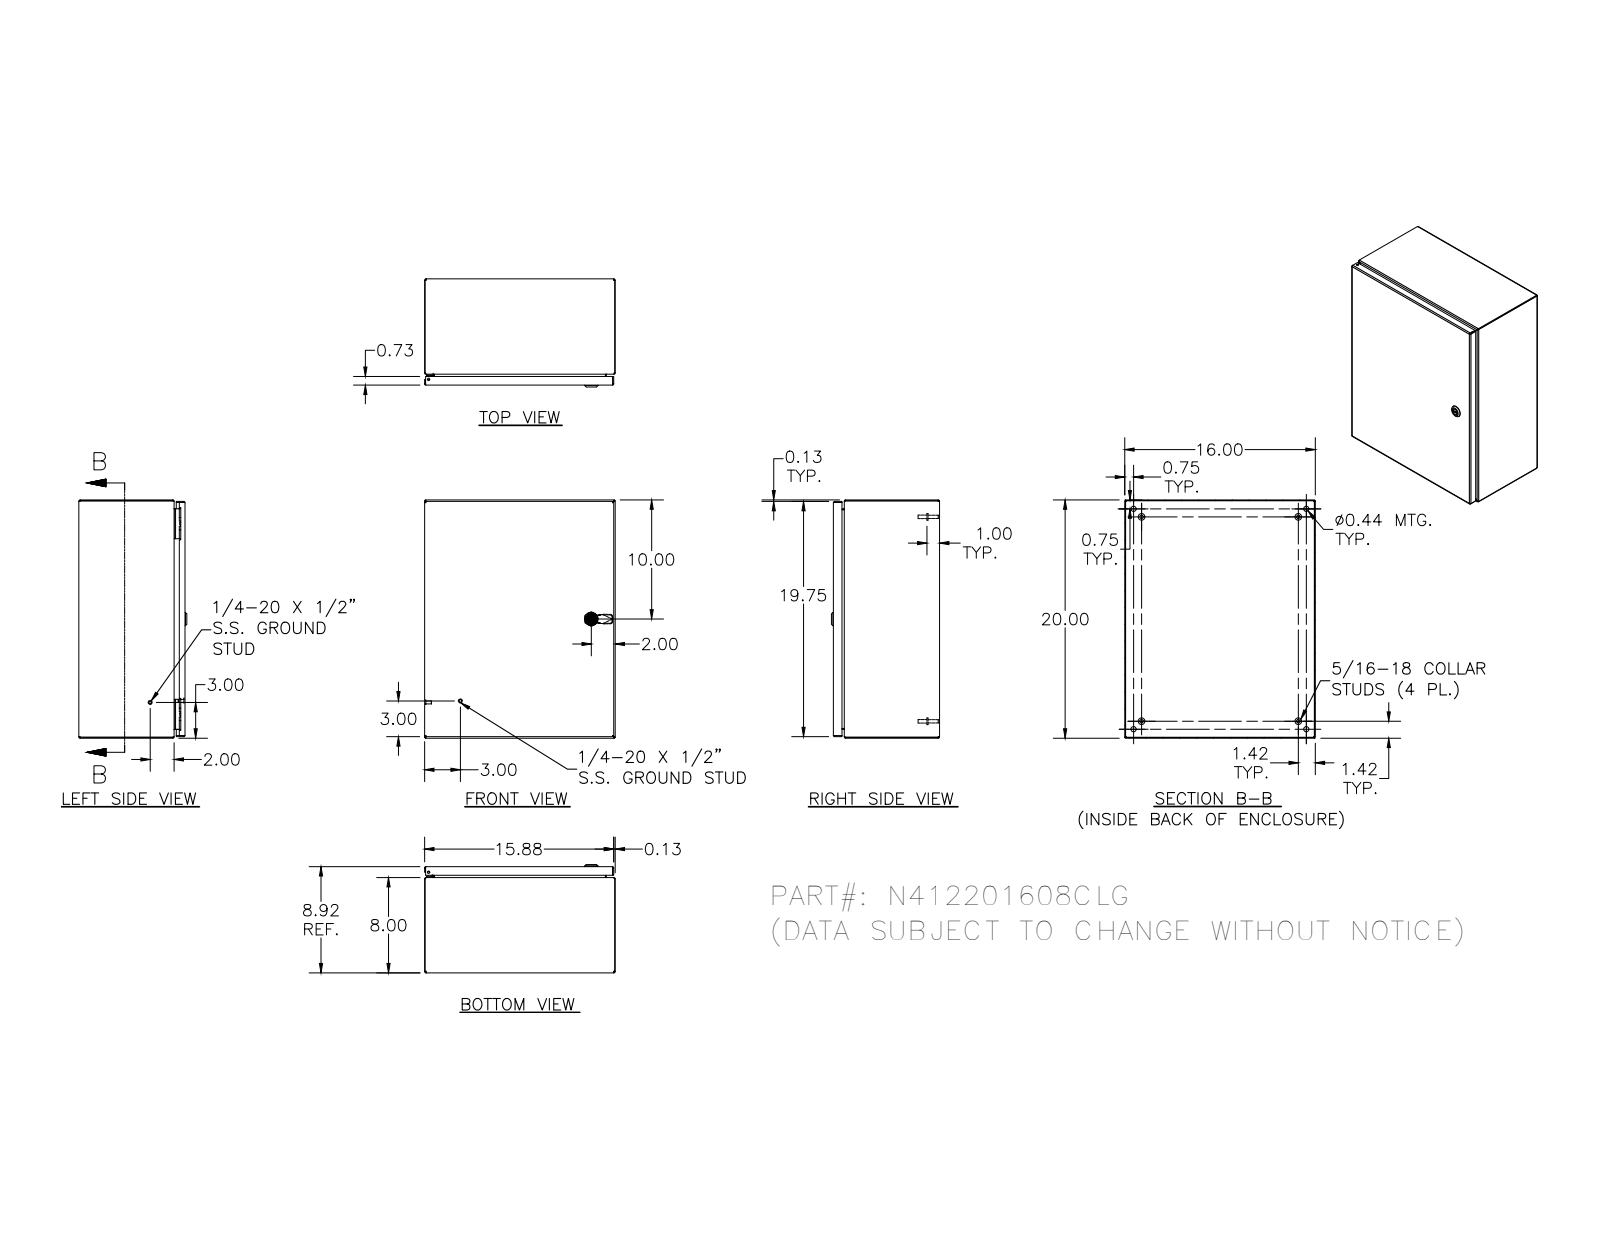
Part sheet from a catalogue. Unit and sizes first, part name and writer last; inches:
Units: inches
Overall size (bounding box): 20 × 16 × 9.075
Round holes (diameter × count): ⌀0.188 ×5, ⌀0.093 ×4, ⌀0.152 ×4, ⌀0.167 ×4, ⌀0.172 ×4, ⌀0.437 ×4, ⌀0.156 ×2, ⌀0.187 ×1, ⌀0.197 ×1, ⌀0.315 ×1, ⌀0.394 ×1, ⌀0.402 ×1
Round bosses / shafts (diameter × count): ⌀0.25 ×10, ⌀0.131 ×5, ⌀0.563 ×4, ⌀0.36 ×4, ⌀0.32 ×4, ⌀0.3 ×4, ⌀0.275 ×4, ⌀0.256 ×4
Partial cylindrical surfaces — rounded edges, fillets, slot ends (radius × count): R0.012 ×30, R0.031 ×30, R0.05 ×26, R0.105 ×20, R0.016 ×18, R0.125 ×16, R0.02 ×13, R0.032 ×8
Main face-to-face distances: 0.074, 8.843, 8.769, 8.917, 0.074, 15.926, 16, 15.852, 15.926, 19.852
Hole centre spacings: 16, 0.66, 0.656, 1.307, 1.965, 15.34, 16.66, 15.614
Volume: 101 in³ · Surface area: 2 747 in²
Bodies: 33 solids, 1449 faces (530 planar, 547 cylindrical, 372 other)
Part name (STEP PRODUCT): N412201608CLG
STEP written by: SolidWorks 2018 (AUTOMOTIVE_DESIGN)
